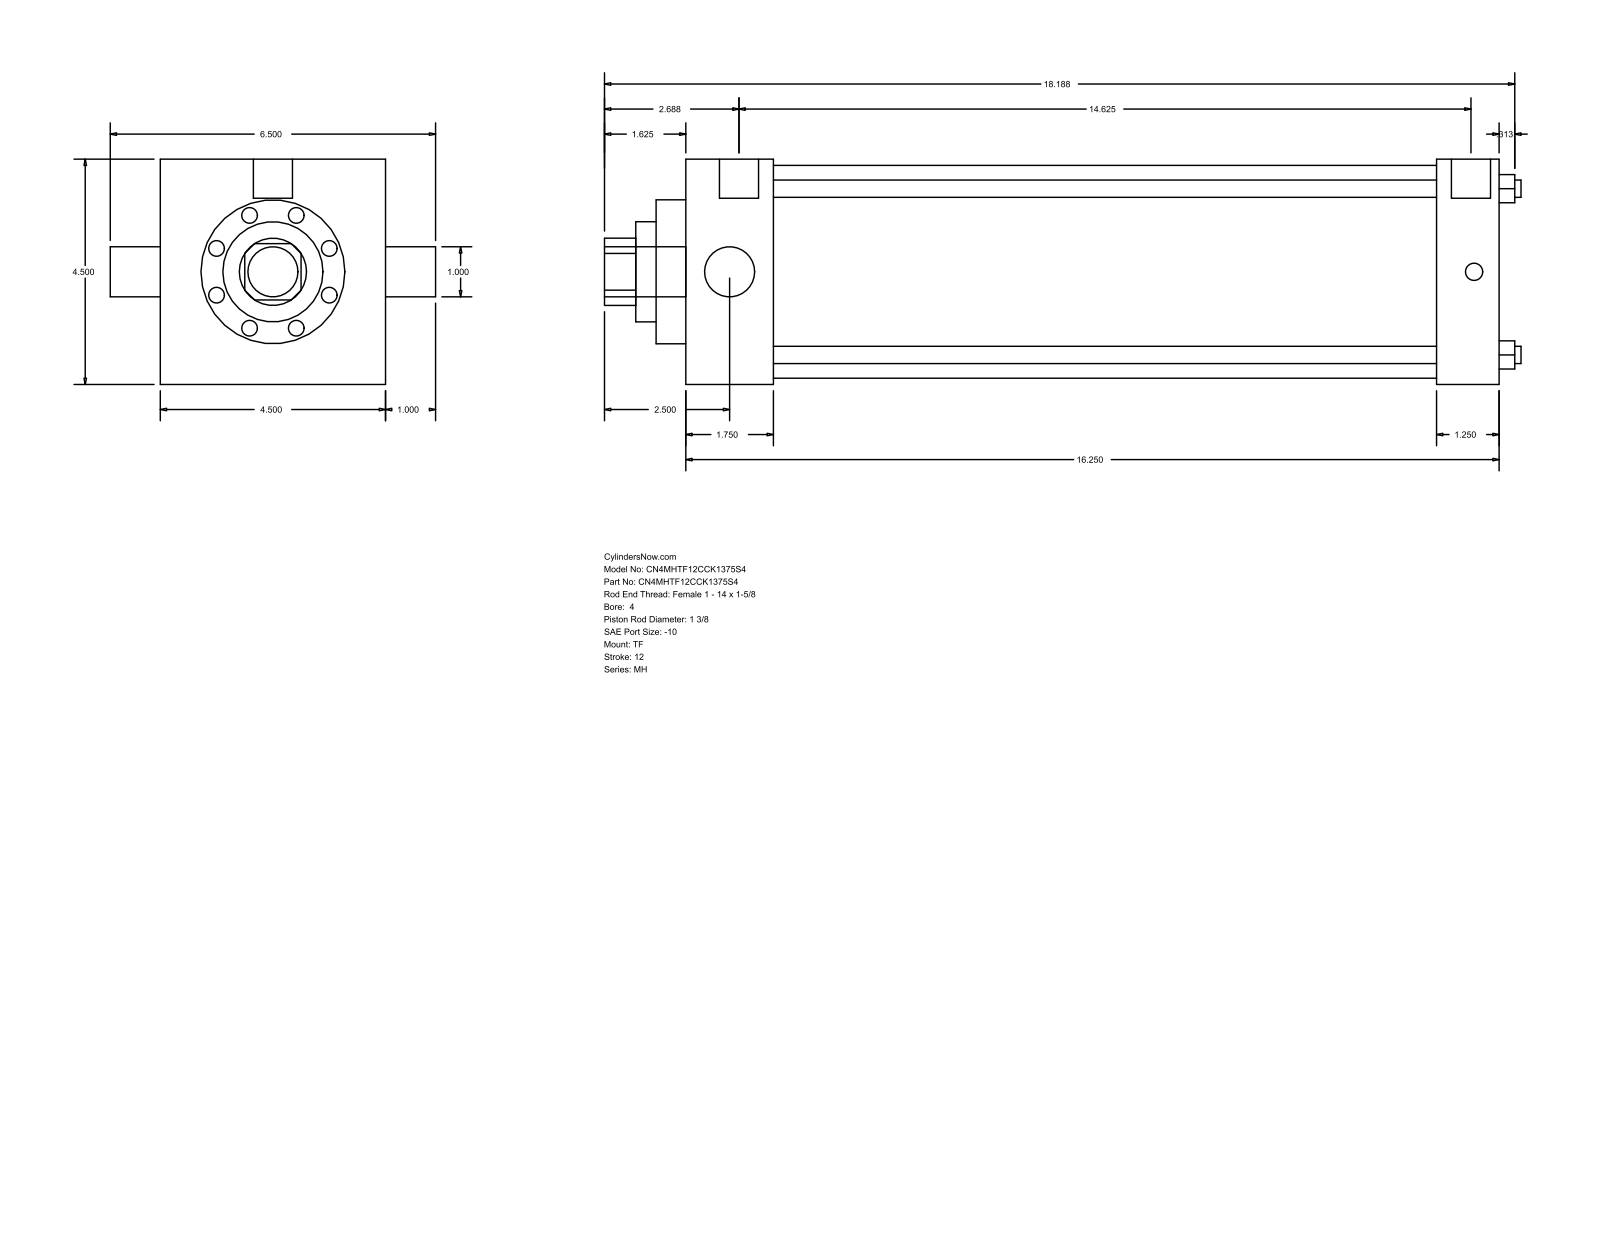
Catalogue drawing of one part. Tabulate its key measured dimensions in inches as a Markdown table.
| quantity | value |
| --- | --- |
| part name | MH_TF__0400_1.375 |
| STEP written by | GSSL Pune (CONFIG_CONTROL_DESIGN) |
| units | inches |
| bodies | 0 solids, 86 faces (61 planar, 25 cylindrical, 0 other) |
| overall size | 18.313 × 6.5 × 4.5 |
| round holes (diameter × count) | 0.345 × 4, 1 × 1, 1.375 × 1, 2 × 1, 2.875 × 1, 4.25 × 1 |
| round bosses / shafts (diameter × count) | 0.344 × 3, 0.781 × 2, 1 × 1 |
| partial cylindrical surfaces (radius × count) | 0.672 × 1 |
| main face-to-face distances | 4.5, 16.25, 1.75, 14.5, 15, 13.25, 1.25, 0.594, 2.344, 15.594 |
| hole center spacings | 2.347, 3.32, 4.695 |
